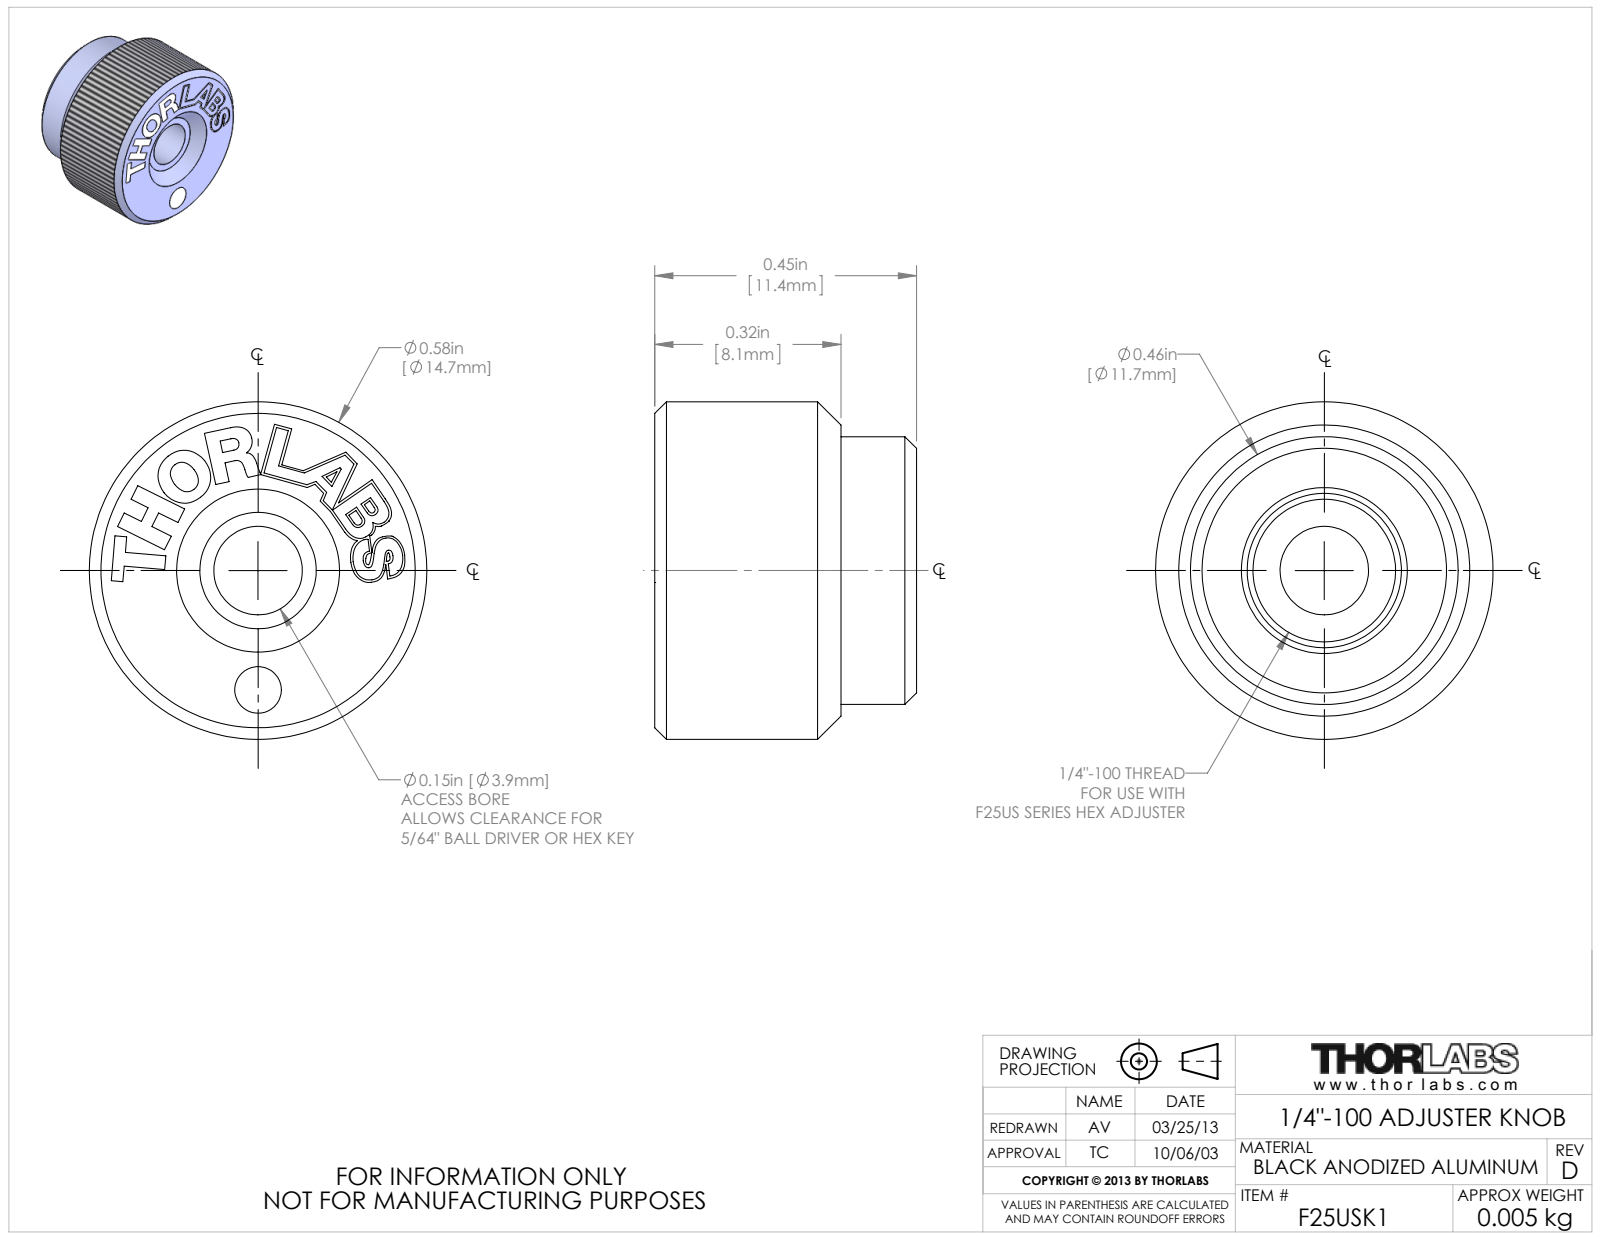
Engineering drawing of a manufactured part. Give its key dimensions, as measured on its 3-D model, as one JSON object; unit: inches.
{"part_name": "7644-E0W", "step_written_by": "SolidWorks 2012 (AUTOMOTIVE_DESIGN)", "units": "inches", "bodies": {"solids": 1, "faces": 208, "planar": 118, "cylindrical": 19, "other": 71}, "overall_size": [0.58, 0.58, 0.45], "volume_in3": 0.088, "surface_area_in2": 1.48, "round_holes": [[0.08, 1], [0.152, 1], [0.245, 1], [0.265, 1], [0.29, 1]], "round_bosses_or_shafts": [[0.58, 1], [0.46, 1]], "partial_cylinders_radius": [[0.014, 1], [0.047, 1], [0.059, 1]], "face_to_face_distances": [0.45, 0.27, 0.18, 0.32, 0.05, 0.13, 0.04, 0.31, 0.14, 0.04], "hole_center_spacings": [0.205]}
